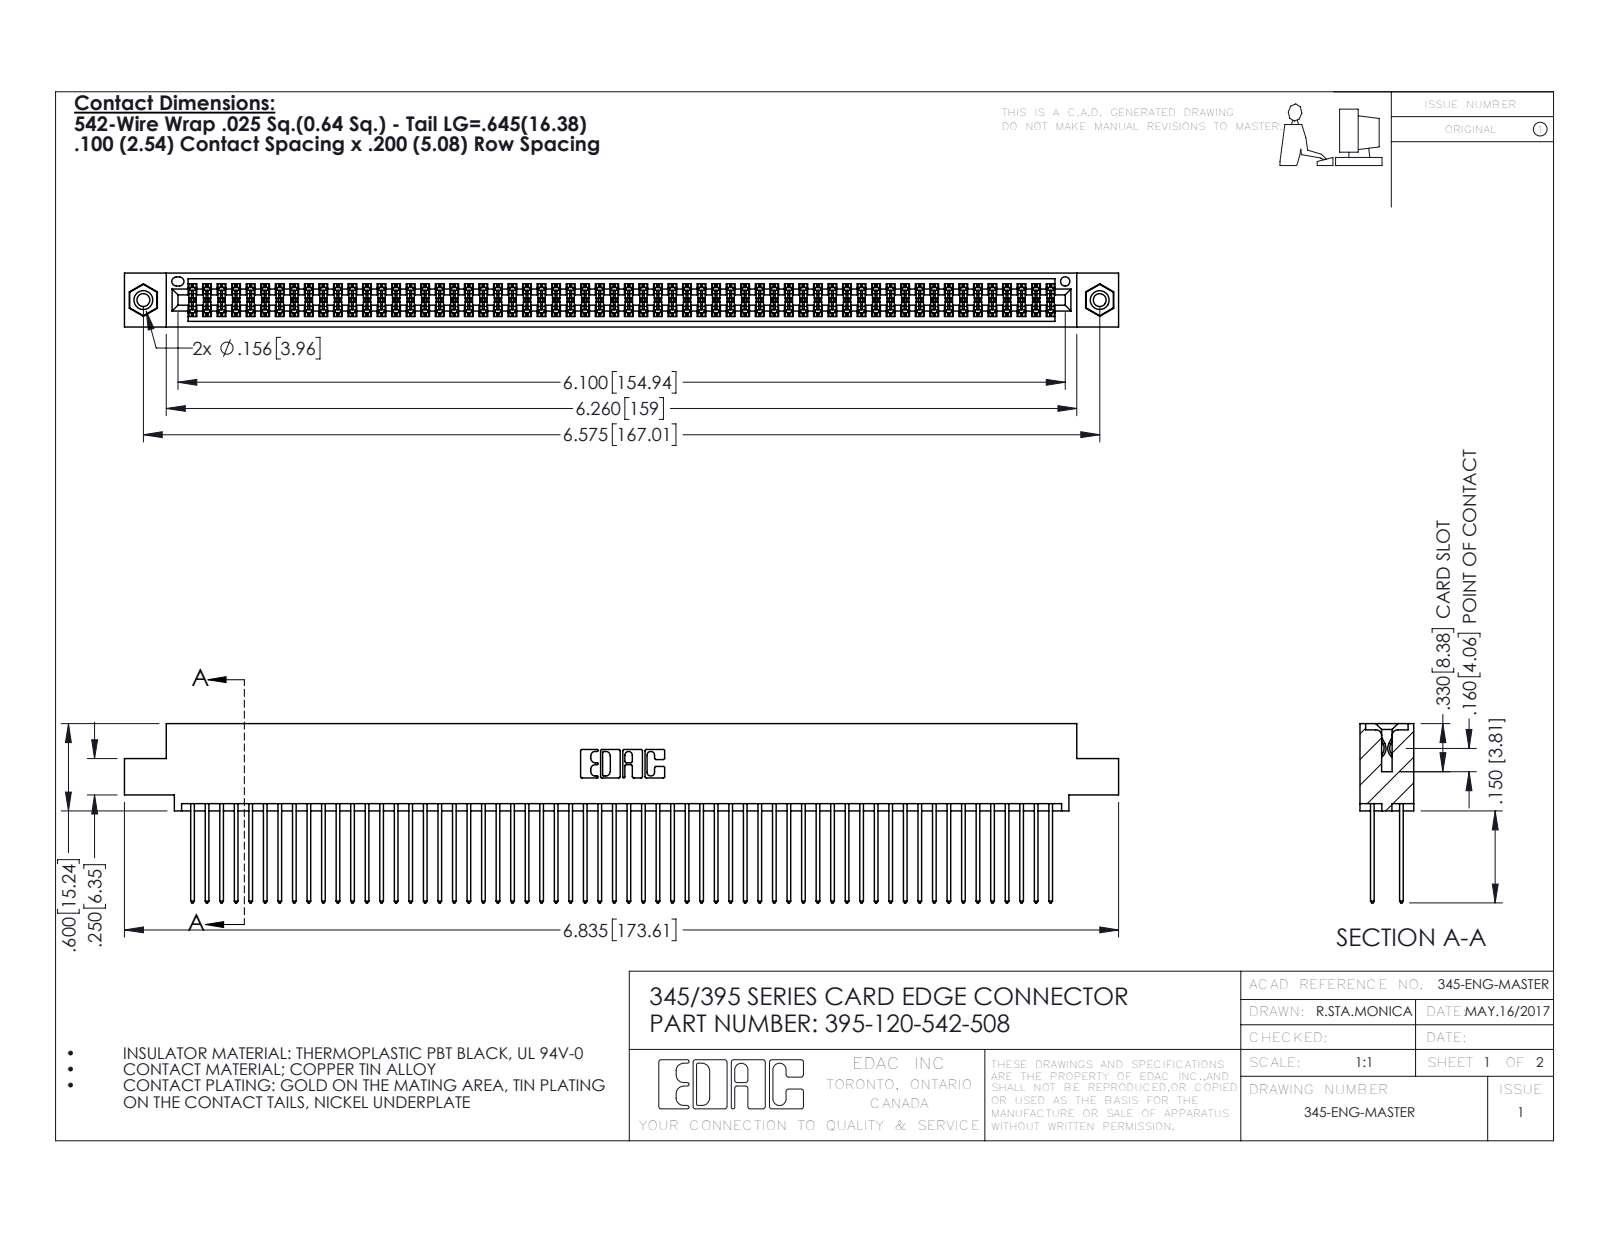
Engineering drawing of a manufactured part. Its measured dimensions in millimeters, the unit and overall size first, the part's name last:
Units: millimetres
Overall size (bounding box): 173.6 × 31.3 × 9.4
Round holes (diameter × count): ⌀2.3 ×2, ⌀3.2 ×2, ⌀4 ×2, ⌀1.6 ×1
Round bosses / shafts (diameter × count): ⌀3.9 ×2
Partial cylindrical surfaces — rounded edges, fillets, slot ends (radius × count): R0.2 ×180, R0.3 ×120, R0.3 ×22, R0.2 ×6, R0.8 ×6, R0.7 ×3, R0.4 ×2, R0.5 ×2
Main face-to-face distances: 1.8, 7.6, 5.1, 2.5, 6.9, 0.6, 5.7, 9.4, 4.4, 3.8
Hole centre spacings: 6.9, 161, 167
Volume: 17 520 mm³ · Surface area: 28 950 mm²
Bodies: 123 solids, 6190 faces (4076 planar, 2098 cylindrical, 16 other)
Part name (STEP PRODUCT): 395-120-542-508; 345-292-001_345-293-142; 345-250-001_345-250-003-102; 345 Part_0.110 Offset - 0.156 Dia-TI
STEP written by: SolidWorks 2016 (CONFIG_CONTROL_DESIGN)
